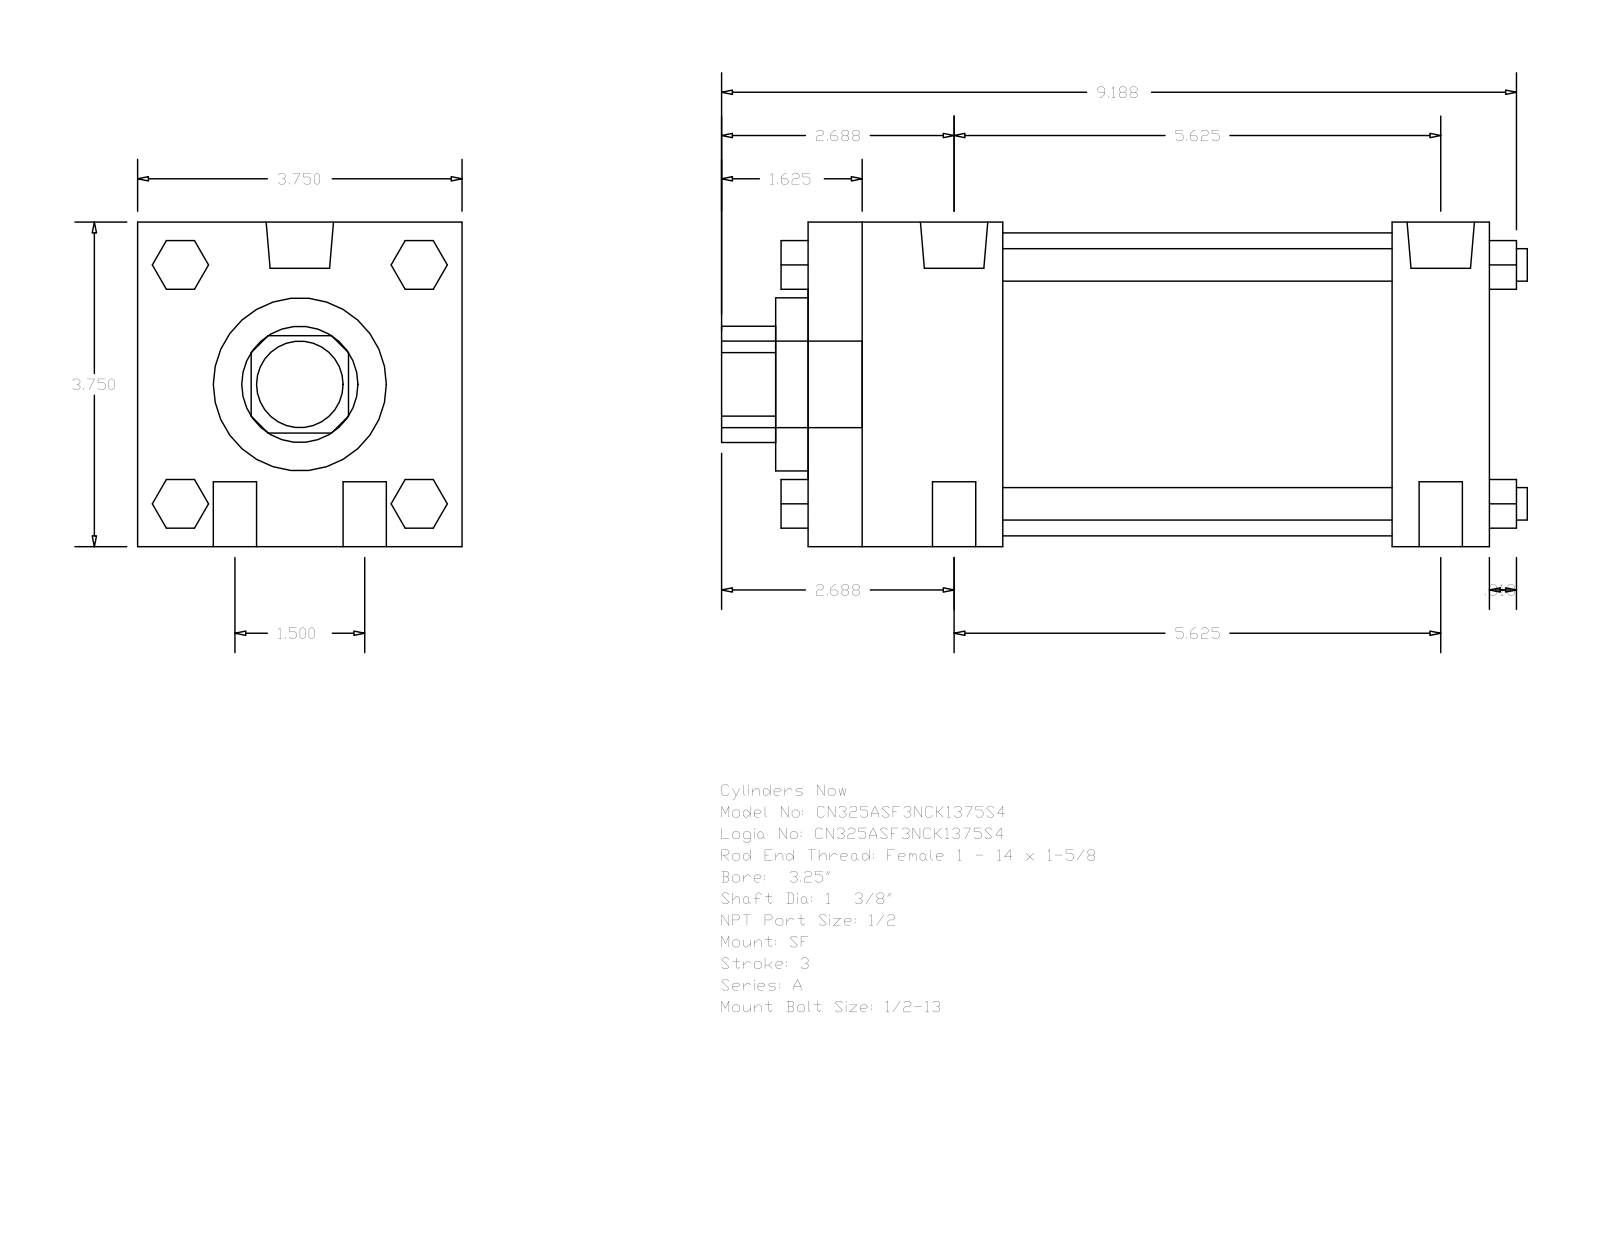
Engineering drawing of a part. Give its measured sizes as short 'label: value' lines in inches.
name: A_SF__0325_1.375
written by: GSSL Pune (CONFIG_CONTROL_DESIGN)
unit: in
bodies: 0 solids, 124 faces (94 planar, 30 cylindrical, 0 other)
size: 9.313 × 3.75 × 3.75
holes: 1× ⌀1.375, 1× ⌀2, 1× ⌀3.5
bosses: 4× ⌀0.5, 4× ⌀0.375, 2× ⌀0.778, 2× ⌀0.344, 1× ⌀1
rounds: 1× R0.672
face distances: 3.75, 7.875, 1.125, 6.75, 2.25, 4.5, 5.625, 0.375, 2.625, 7.125
